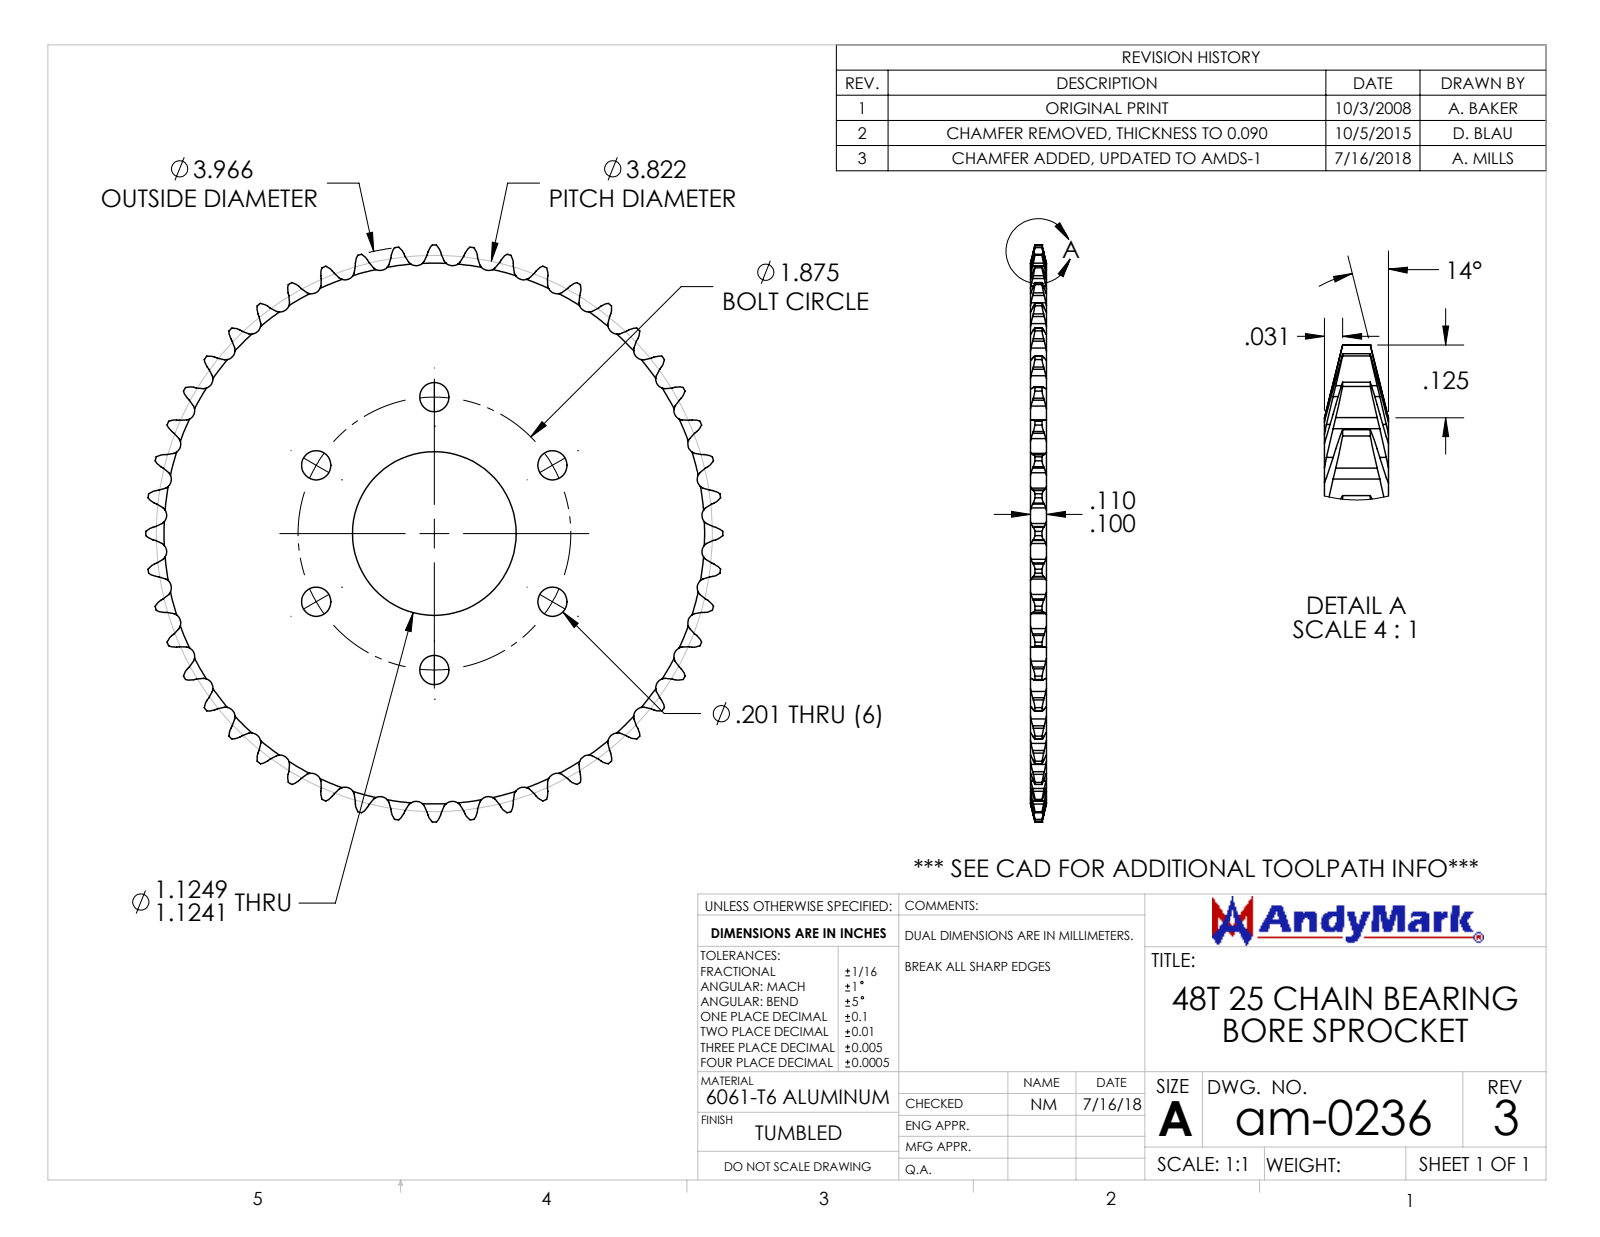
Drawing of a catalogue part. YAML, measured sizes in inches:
part_name: "am-0236_Plate Sprocket"
step_written_by: "SolidWorks 2018 (AUTOMOTIVE_DESIGN)"
units: inches
bodies: {solids: 1, faces: 525, planar: 98, cylindrical: 329, other: 98}
overall_size: [3.966, 3.966, 0.11]
volume: 1.107
surface_area: 22.86
round_holes:
  - {diameter: 0.201, count: 6}
  - {diameter: 1.125, count: 1}
partial_cylinders:
  - {radius: 0.104, count: 96}
  - {radius: 0.171, count: 96}
  - {radius: 0.067, count: 48}
  - {radius: 1.983, count: 1}
face_to_face_distances: [0.11, 1.128, 1.127, 1.128, 1.13]
hole_center_spacings: [0.937, 1.624, 1.875, 0.938]
